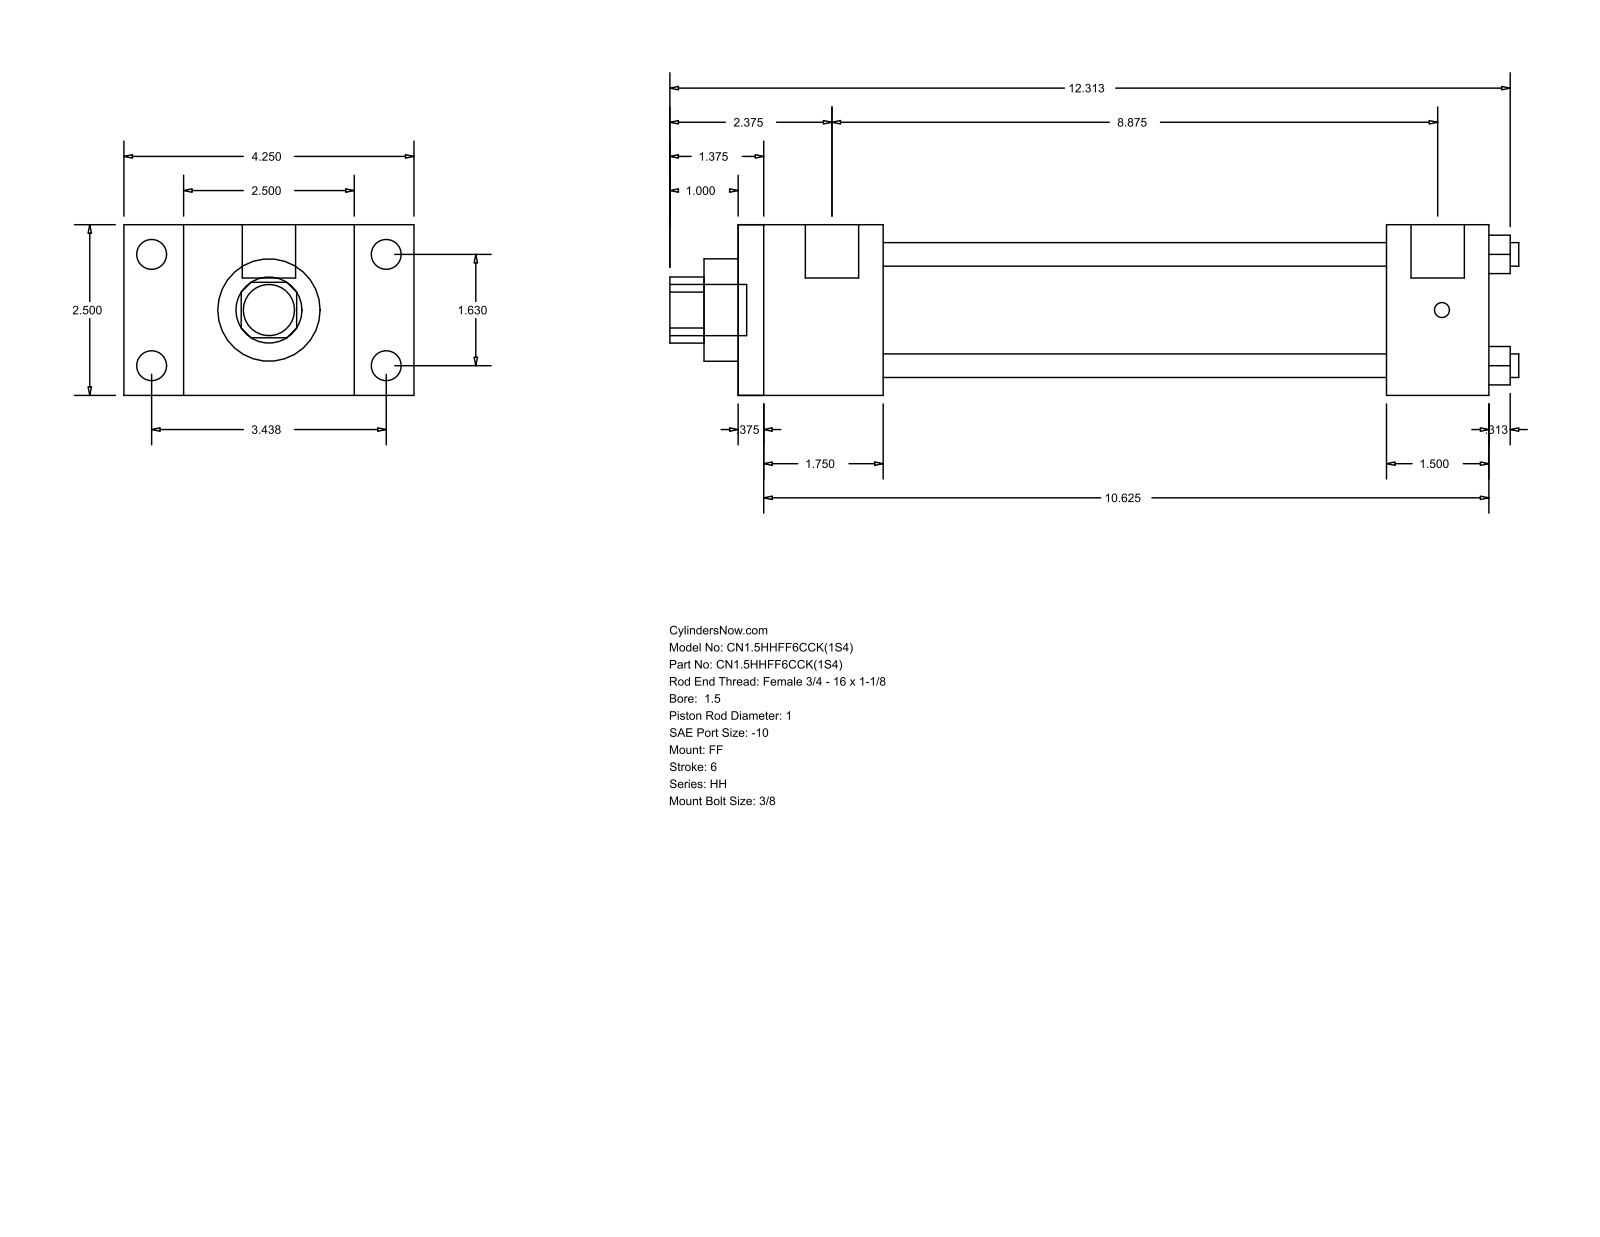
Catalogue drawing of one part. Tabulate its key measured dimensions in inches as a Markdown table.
| quantity | value |
| --- | --- |
| part name | HH_FF__0150_1 |
| STEP written by | GSSL Pune (CONFIG_CONTROL_DESIGN) |
| units | inches |
| bodies | 0 solids, 92 faces (64 planar, 28 cylindrical, 0 other) |
| overall size | 12.437 × 4.25 × 2.5 |
| round holes (diameter × count) | 0.345 × 4, 1 × 1, 1.5 × 1, 1.75 × 1 |
| round bosses / shafts (diameter × count) | 0.438 × 4, 0.219 × 4, 0.781 × 2, 0.75 × 1 |
| partial cylindrical surfaces (radius × count) | 0.484 × 1 |
| main face-to-face distances | 2.5, 11, 0.375, 10.625, 2.125, 1.75, 8.875, 9.5, 9.125, 7.375 |
| hole center spacings | 1.152, 1.63, 2.305 |
